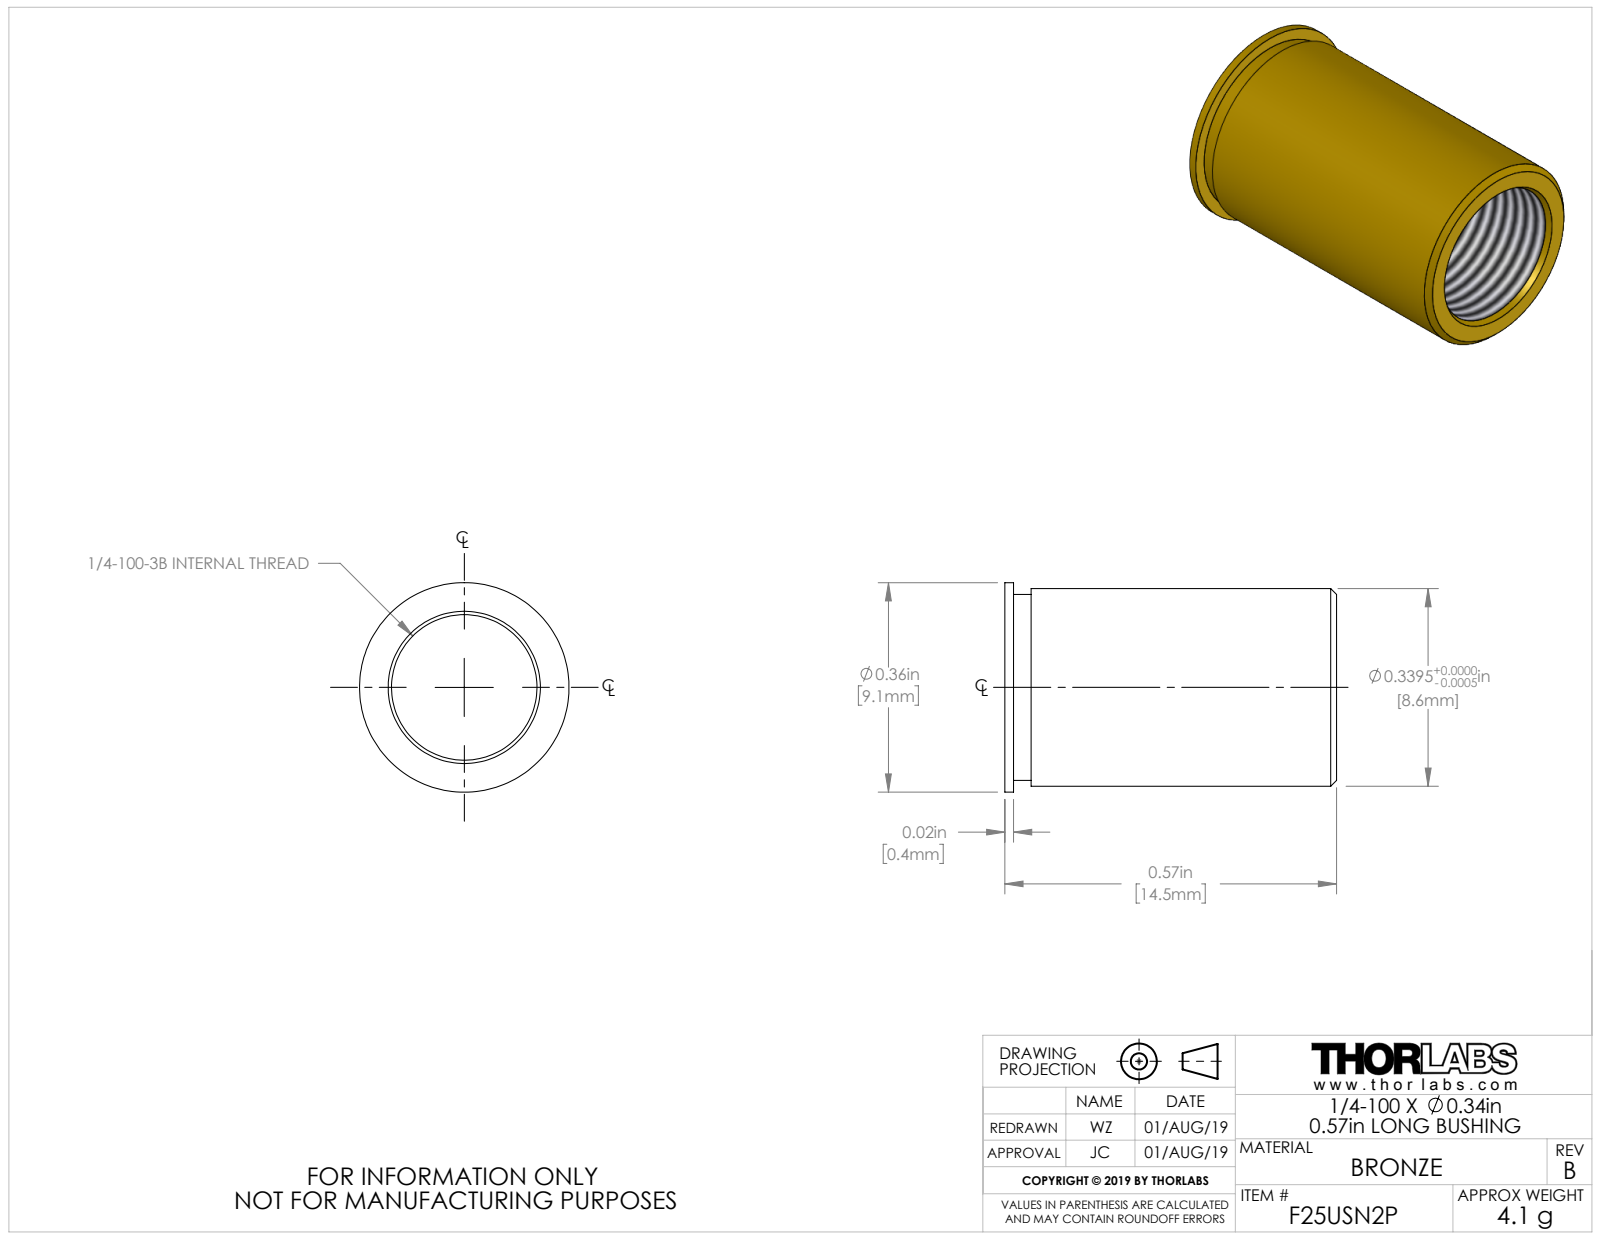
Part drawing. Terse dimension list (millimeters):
name: 18994-E0W
written by: SolidWorks 2007 (AUTOMOTIVE_DESIGN)
unit: mm
bodies: 1 solid, 18 faces (4 planar, 8 cylindrical, 6 other)
size: 14.48 × 9.14 × 9.14
volume: 383 mm³; area: 754 mm²
holes: 1× ⌀6.35
bosses: 1× ⌀9.14, 1× ⌀8.62, 1× ⌀8.12
face distances: 14.48, 0.38, 14.1, 1.14, 0.76, 13.34
